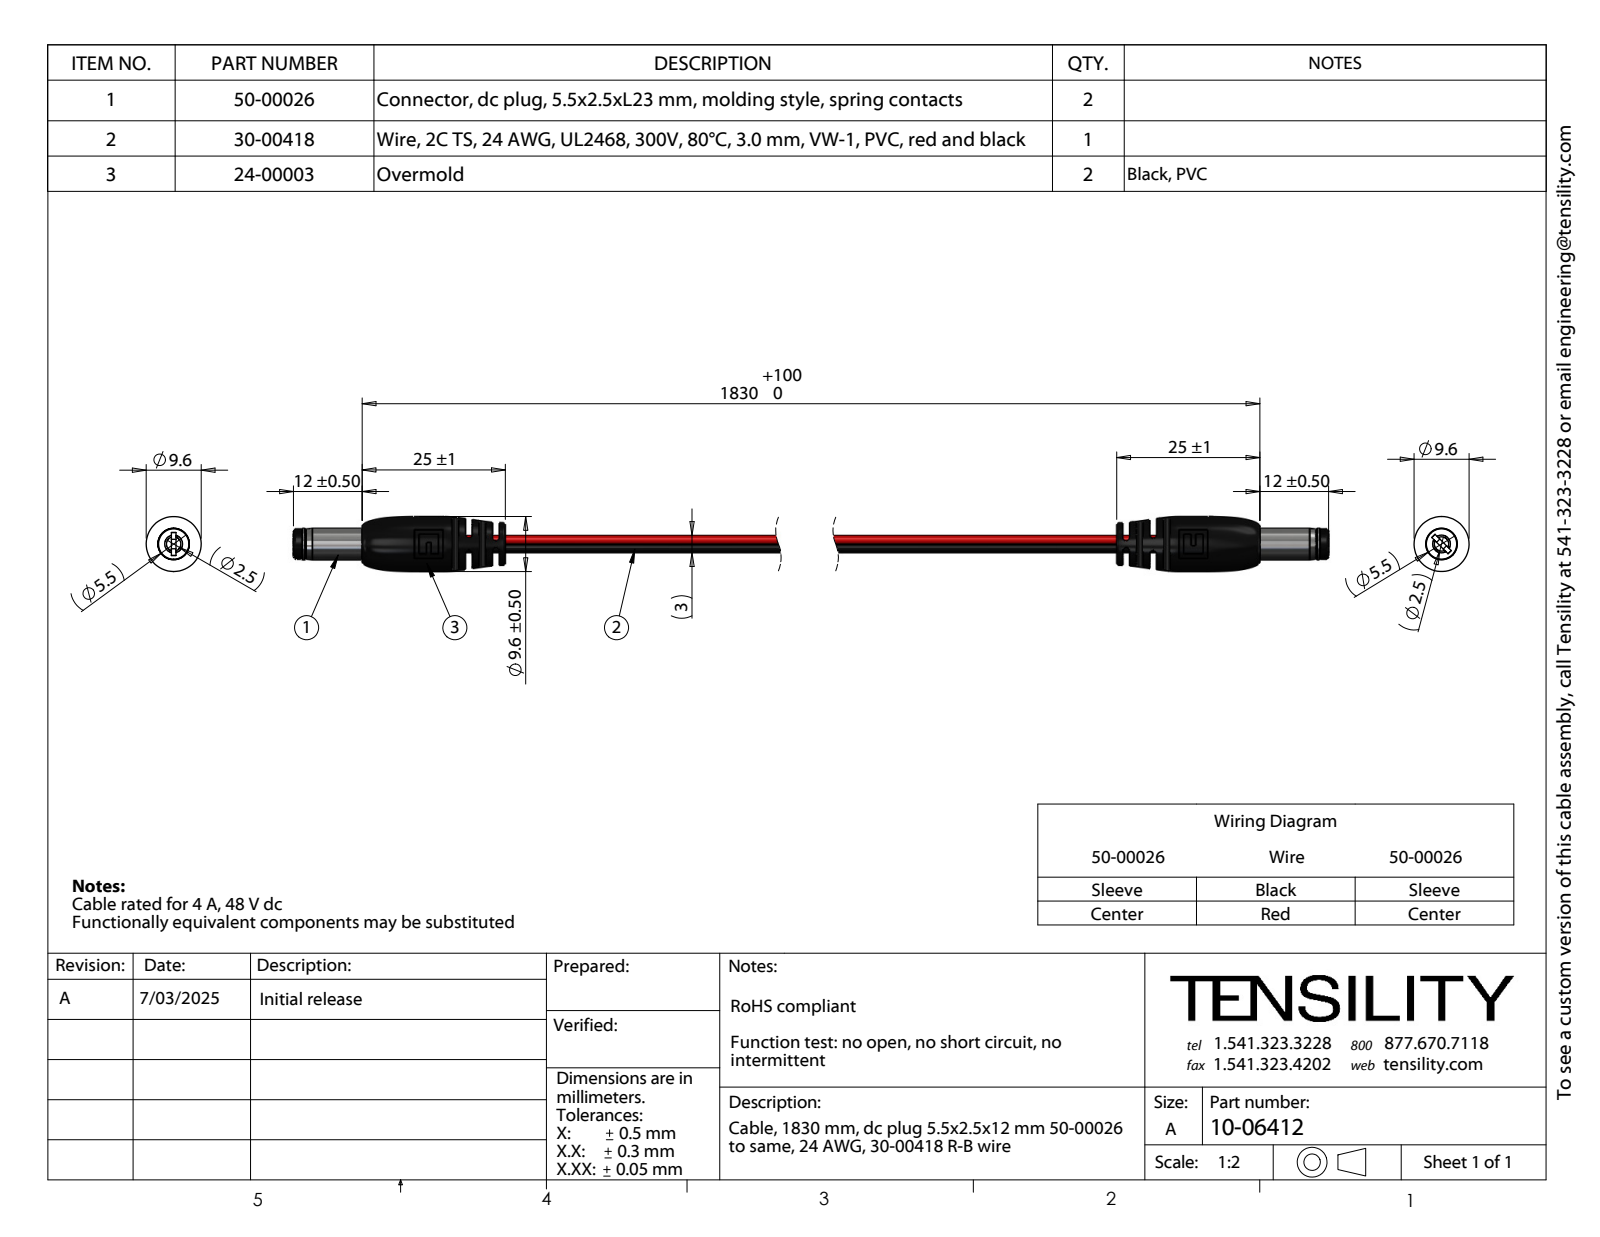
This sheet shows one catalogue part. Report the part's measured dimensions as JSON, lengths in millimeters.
{"part_name": "10-06412_revA; 24-00003; 50-00026; 50-00026 insulator (+3 more)", "step_written_by": "SolidWorks 2025 (CONFIG_CONTROL_DESIGN)", "units": "millimeters", "bodies": {"solids": 31, "faces": 710, "planar": 206, "cylindrical": 226, "other": 278}, "overall_size": [205.36, 9.6, 9.6], "volume_mm3": 3621, "surface_area_mm2": 9518, "round_holes": [[2.5, 1], [4.8, 1], [5.5, 1]], "round_bosses_or_shafts": [[9.6, 1], [5.51, 1], [5.3, 1]], "partial_cylinders_radius": [[0.2, 20], [0.15, 16], [0.59, 16], [0.3, 4], [0.4, 4], [1.05, 4], [1.25, 4], [1.29, 2]], "face_to_face_distances": [1.18, 2.36, 3.54, 4.72, 141.74, 142.92, 140.56, 0.8, 144.1, 5.9], "hole_center_spacings": [0.31, 0.35, 1.45, 0.32, 0.36, 0.43, 0.51, 1.46]}
